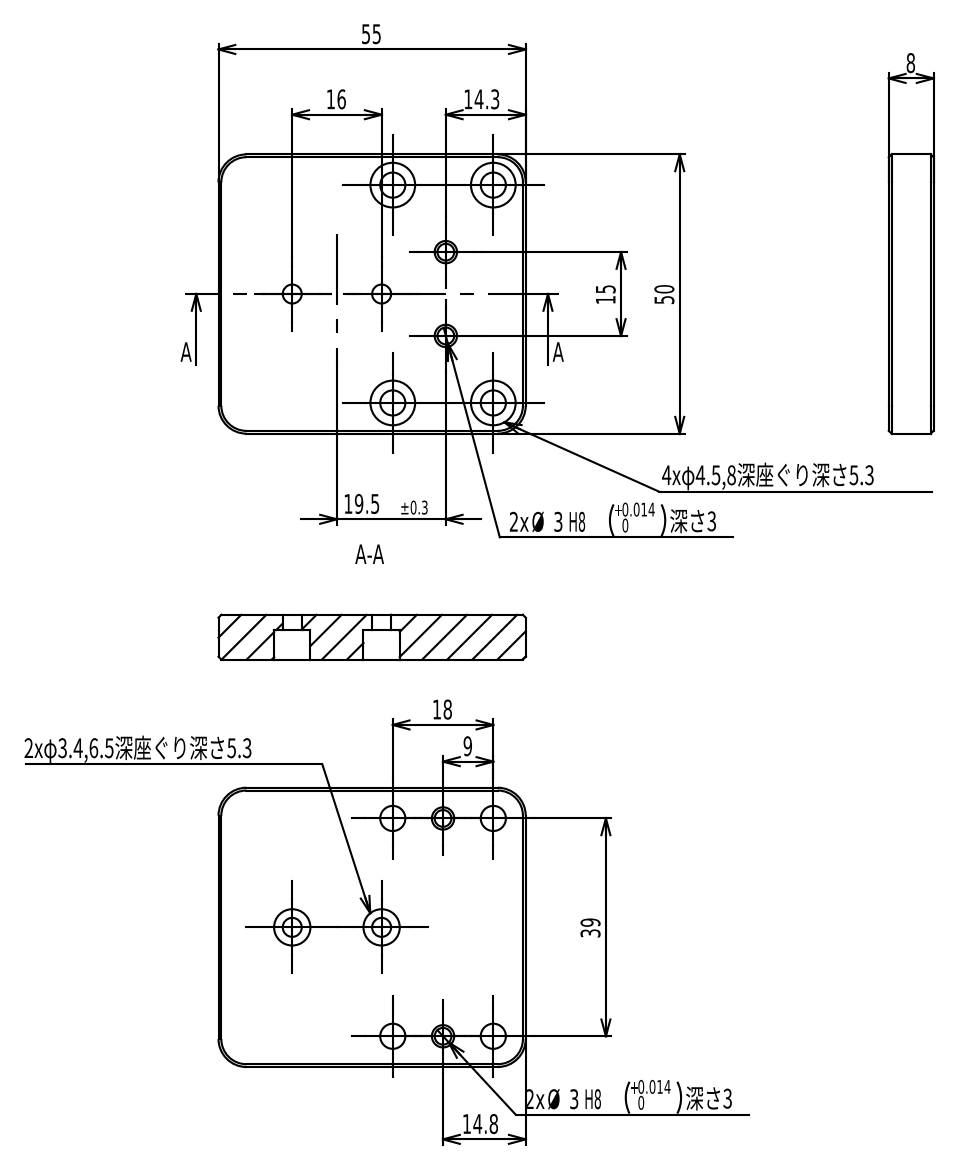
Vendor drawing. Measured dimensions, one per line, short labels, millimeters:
name: PDG60-4-1
written by: SolidWorks 2020 (CONFIG_CONTROL_DESIGN)
unit: mm
bodies: 1 solid, 76 faces (24 planar, 36 cylindrical, 16 other)
size: 55 × 50 × 8
volume: 20 050 mm³; area: 7 849 mm²
holes: 4× ⌀3, 4× ⌀4.5, 4× ⌀8, 2× ⌀3.4, 2× ⌀6.5
rounds: 4× R5
face distances: 8, 50, 55, 2.7, 5.3, 40.3, 43.83, 2.6, 3, 5
hole spacings: 9, 40.02, 39, 12.01, 13.73, 14.71, 15.31, 18
